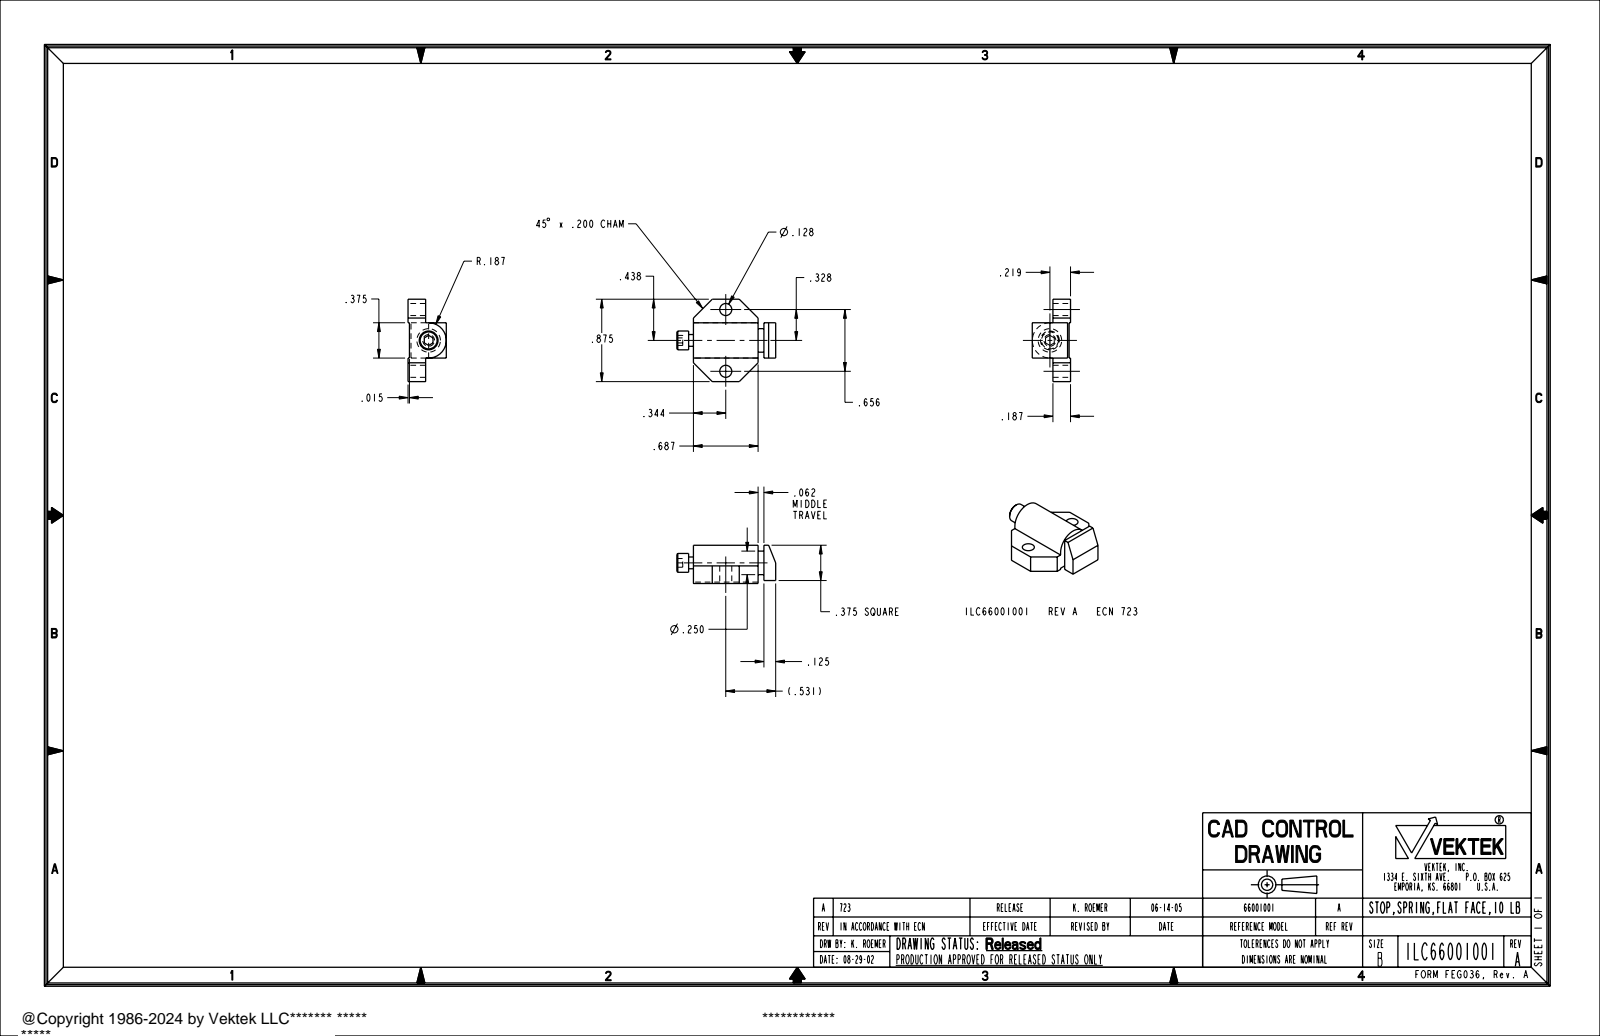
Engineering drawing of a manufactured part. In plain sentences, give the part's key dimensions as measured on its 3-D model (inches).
The part is named "ILC66001001". Its 3-D file was written by "PRO/ENGINEER BY PARAMETRIC TECHNOLOGY CORPORATION, 2004290 (AUTOMOTIVE_DESIGN_CC2)". It is 1 solid with 46 faces: 33 planar, 11 cylindrical and 2 other. Overall it measures 1.05 by 0.875 by 0.406 inches. Its volume is 0.157 cubic inches and its surface area 2.507 square inches. Round holes: 2 of diameter 0.128. Round bosses or shafts: 1 of diameter 0.25, 1 of diameter 0.2, 1 of diameter 0.125. Partial cylindrical surfaces (rounded edges, fillets, slot ends): 1 of radius 0.187. The main face-to-face distances are 0.187, 0.172, 0.015, 0.821, 0.687, 0.25, 0.625, 0.062, 0.749, 0.125. The hole center spacings are 0.656.
